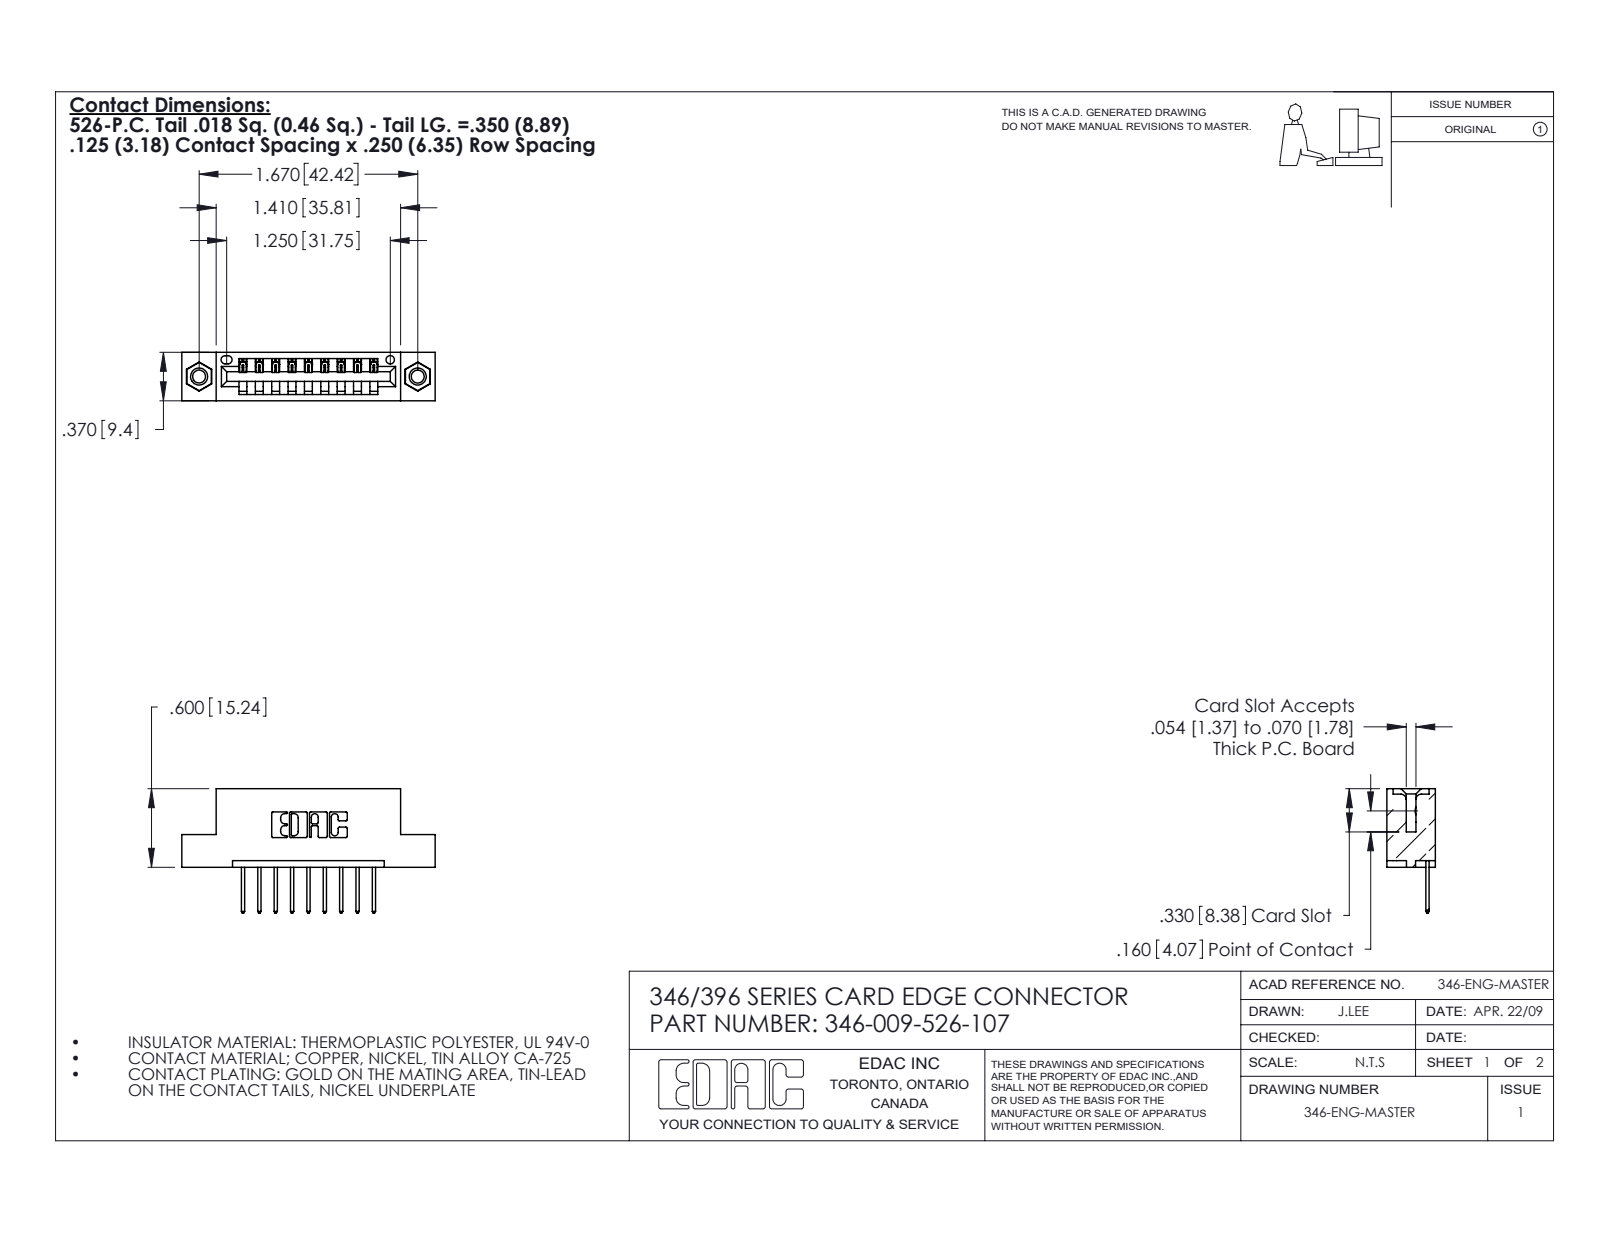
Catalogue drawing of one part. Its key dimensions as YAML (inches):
part_name: "346 Part_Flush Mounting Lugs - 0.156 Dia-TI; 345-250-001_345-250-005-103; 346-009-526-107; 345-292-001_345-293-126"
step_written_by: "SolidWorks 2020 (CONFIG_CONTROL_DESIGN)"
units: inches
bodies: {solids: 12, faces: 704, planar: 468, cylindrical: 220, other: 16}
overall_size: [1.935, 0.95, 0.37]
volume: 0.272
surface_area: 8.122
round_holes:
  - {diameter: 0.098, count: 2}
  - {diameter: 0.125, count: 2}
  - {diameter: 0.156, count: 2}
  - {diameter: 0.064, count: 1}
round_bosses_or_shafts:
  - {diameter: 0.155, count: 2}
partial_cylinders:
  - {radius: 0.01, count: 22}
  - {radius: 0.006, count: 18}
  - {radius: 0.01, count: 18}
  - {radius: 0.007, count: 6}
  - {radius: 0.031, count: 6}
  - {radius: 0.026, count: 3}
  - {radius: 0.031, count: 2}
  - {radius: 0.04, count: 2}
face_to_face_distances: [0.25, 0.37, 0.048, 0.322, 0.072, 0.298, 0.025, 0.148, 0.222, 0.1]
hole_center_spacings: [0.246, 1.465, 1.67]
